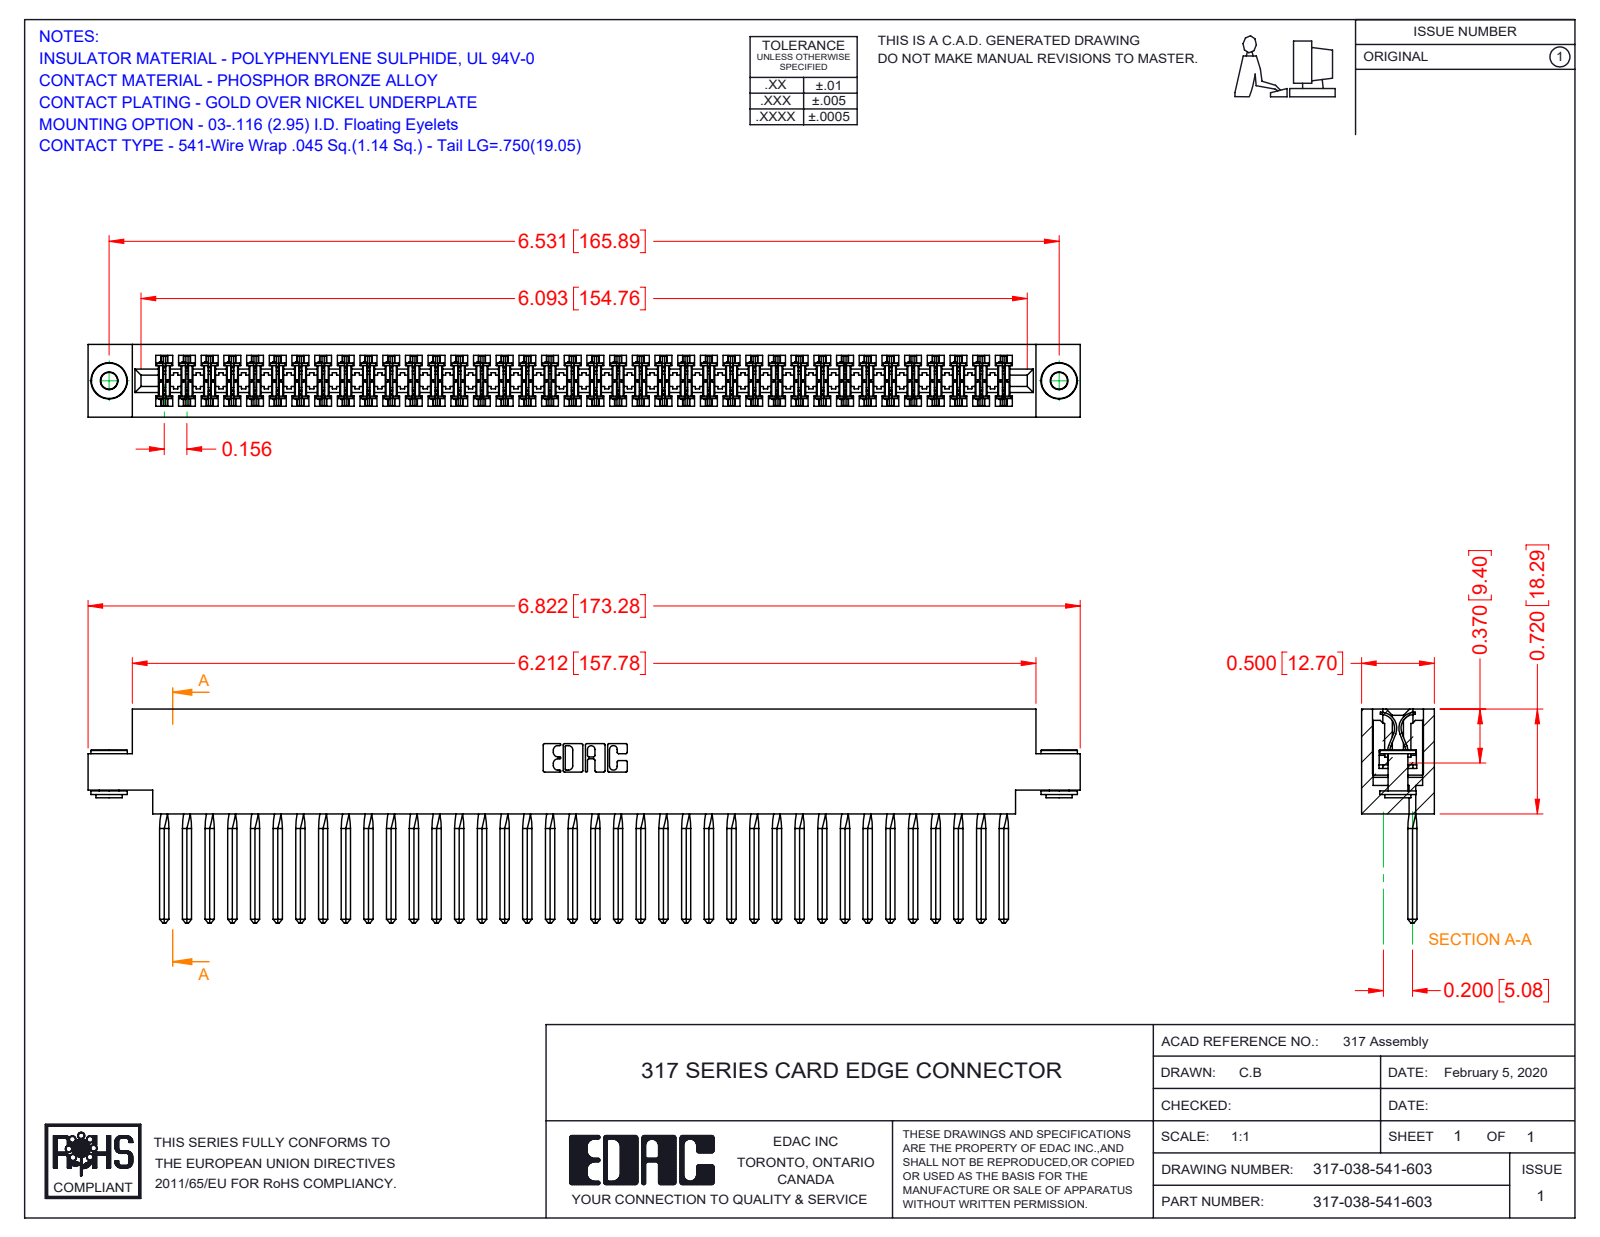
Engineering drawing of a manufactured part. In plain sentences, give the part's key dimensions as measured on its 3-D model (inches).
The part is named "317 Part_.156 Dia - TH; 317-038-541-603; 317-290-002_541; 345-250-002_345-250-002-102". Its 3-D file was written by "SolidWorks 2016 (CONFIG_CONTROL_DESIGN)". It is 41 solids with 5916 faces: 4780 planar, 976 cylindrical and 160 other. Overall it measures 6.822 by 1.47 by 0.5 inches. Its volume is 1.708 cubic inches and its surface area 61.45 square inches. Round holes: 2 of diameter 0.116, 2 of diameter 0.156. Round bosses or shafts: 2 of diameter 0.25, 2 of diameter 0.18, 2 of diameter 0.136. Partial cylindrical surfaces (rounded edges, fillets, slot ends): 76 of radius 0.015, 22 of radius 0.01, 6 of radius 0.007, 6 of radius 0.031, 3 of radius 0.026, 2 of radius 0.095, 2 of radius 0.1, 2 of radius 0.11. The main face-to-face distances are 0.5, 0.075, 0.425, 0.35, 0.195, 0.11, 0.72, 0.115, 0.211, 0.289. The hole center spacings are 6.531.
